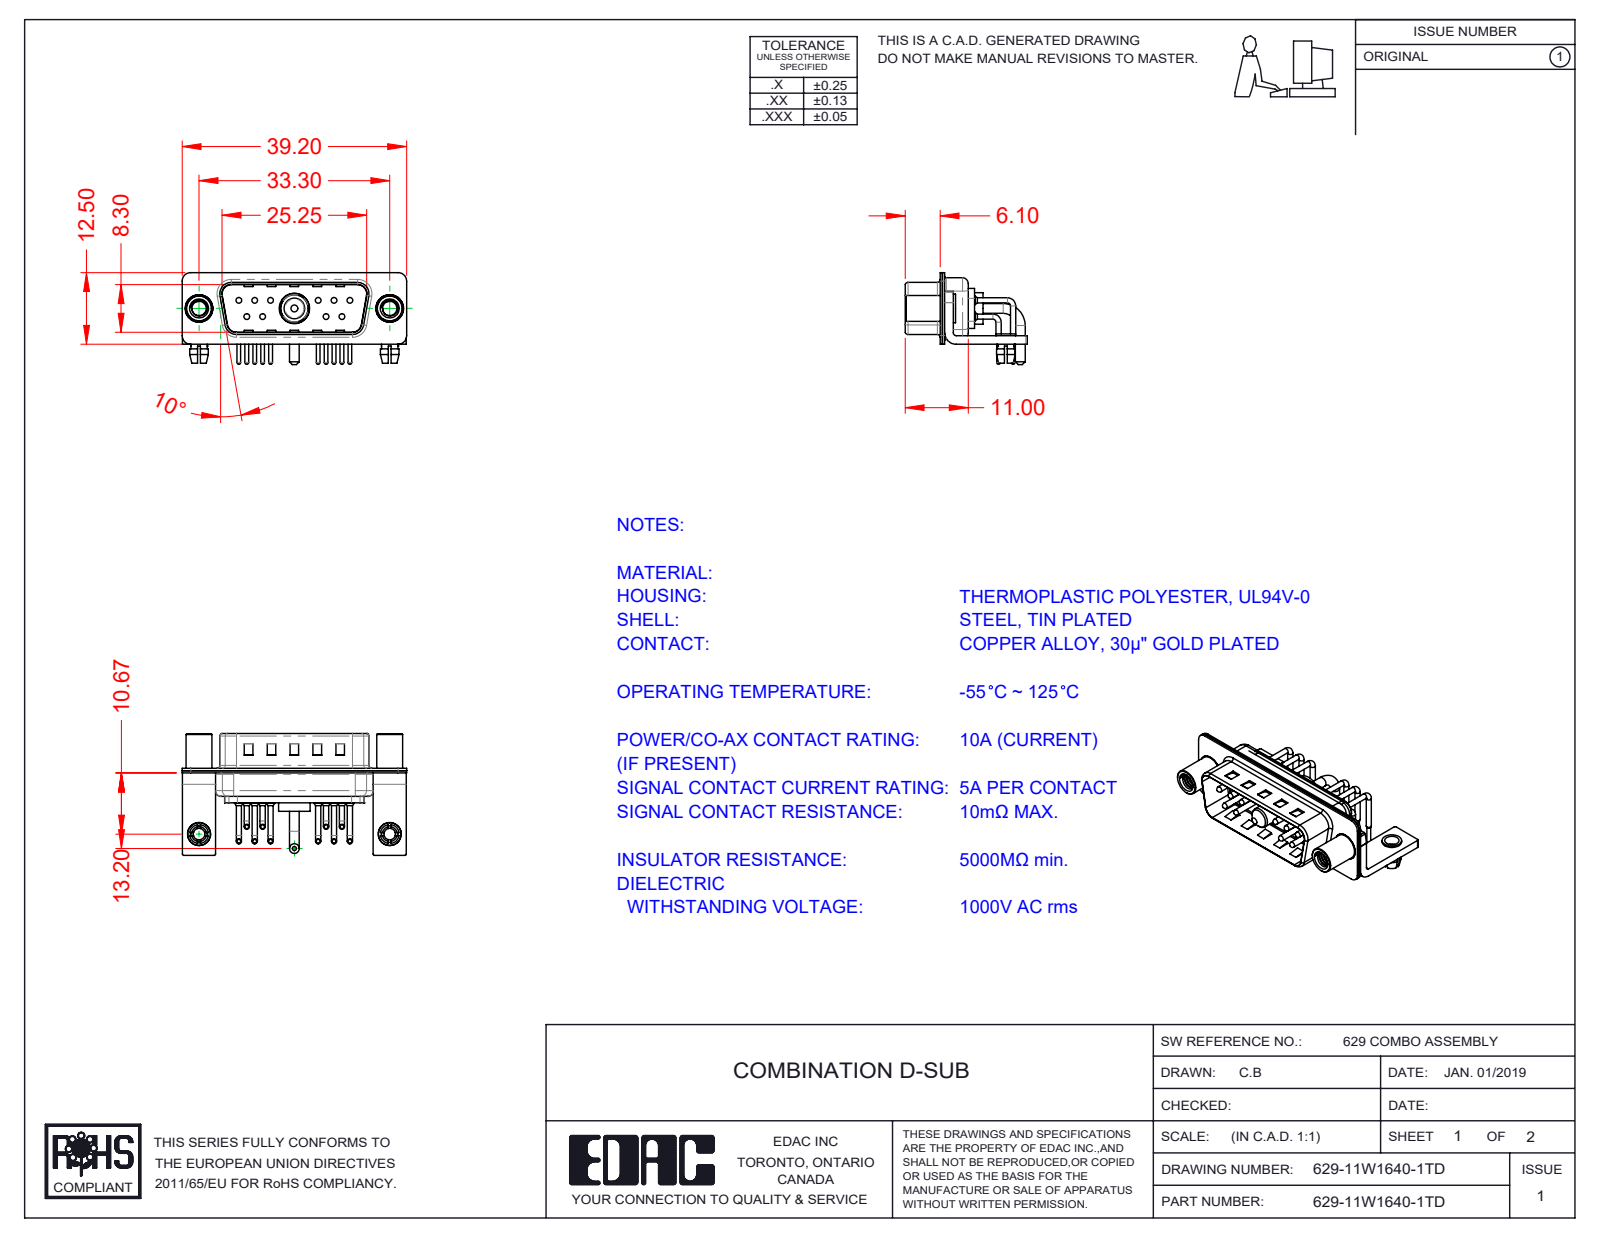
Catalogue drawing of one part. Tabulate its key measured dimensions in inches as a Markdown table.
| quantity | value |
| --- | --- |
| part name | 629Combo Board Lock; 629Combo Shell Rear_15 Contacts; 629-11W1640-1TD; 629Combo Threaded Standoff_D (+6 more) |
| STEP written by | SolidWorks 2020 (CONFIG_CONTROL_DESIGN) |
| units | inches |
| bodies | 21 solids, 1686 faces (868 planar, 622 cylindrical, 196 other) |
| overall size | 1.543 × 0.839 × 0.632 |
| volume | 0.148 in³ |
| surface area | 9.791 in² |
| round holes (diameter × count) | 0.079 × 12, 0.03 × 10, 0.063 × 10, 0.098 × 4, 0.126 × 2, 0.157 × 2, 0.189 × 2, 0.191 × 1, 0.209 × 1 |
| round bosses / shafts (diameter × count) | 0.035 × 20, 0.059 × 10, 0.039 × 10, 0.026 × 10, 0.197 × 2, 0.193 × 2, 0.177 × 2, 0.157 × 2 |
| partial cylindrical surfaces (radius × count) | 0.01 × 16, 0.059 × 16, 0.079 × 13, 0.04 × 10, 0.02 × 9, 0.063 × 8, 0.039 × 7, 0.024 × 4 |
| main face-to-face distances | 0.016, 0.031, 0.059, 0.374, 0.358, 0.343, 0.39, 0.024, 0.075, 0.205 |
| hole center spacings | 0.124, 0.109, 0.545, 0.436, 0.654, 0.198, 0.198, 0.218 |
